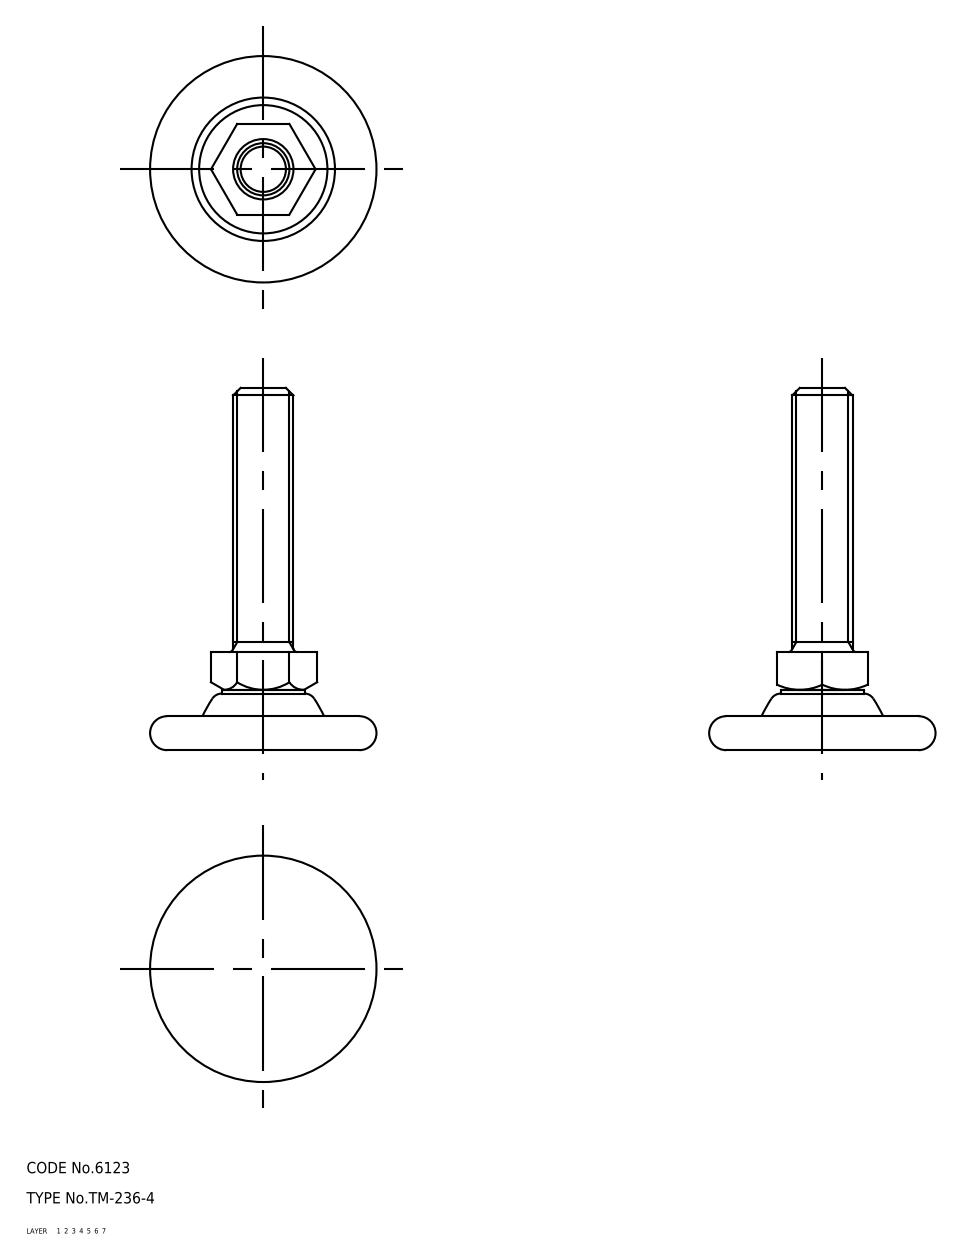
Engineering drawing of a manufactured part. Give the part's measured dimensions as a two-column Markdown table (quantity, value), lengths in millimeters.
| quantity | value |
| --- | --- |
| part name | washer; rubber pad; foot; bolt (+1 more) |
| STEP written by | CADfix (AUTOMOTIVE_DESIGN) |
| units | millimeters |
| bodies | 4 solids, 58 faces (0 planar, 0 cylindrical, 58 other) |
| overall size | 96 × 60 × 60 |
| volume | 40 477 mm³ |
| surface area | 21 196 mm² |
